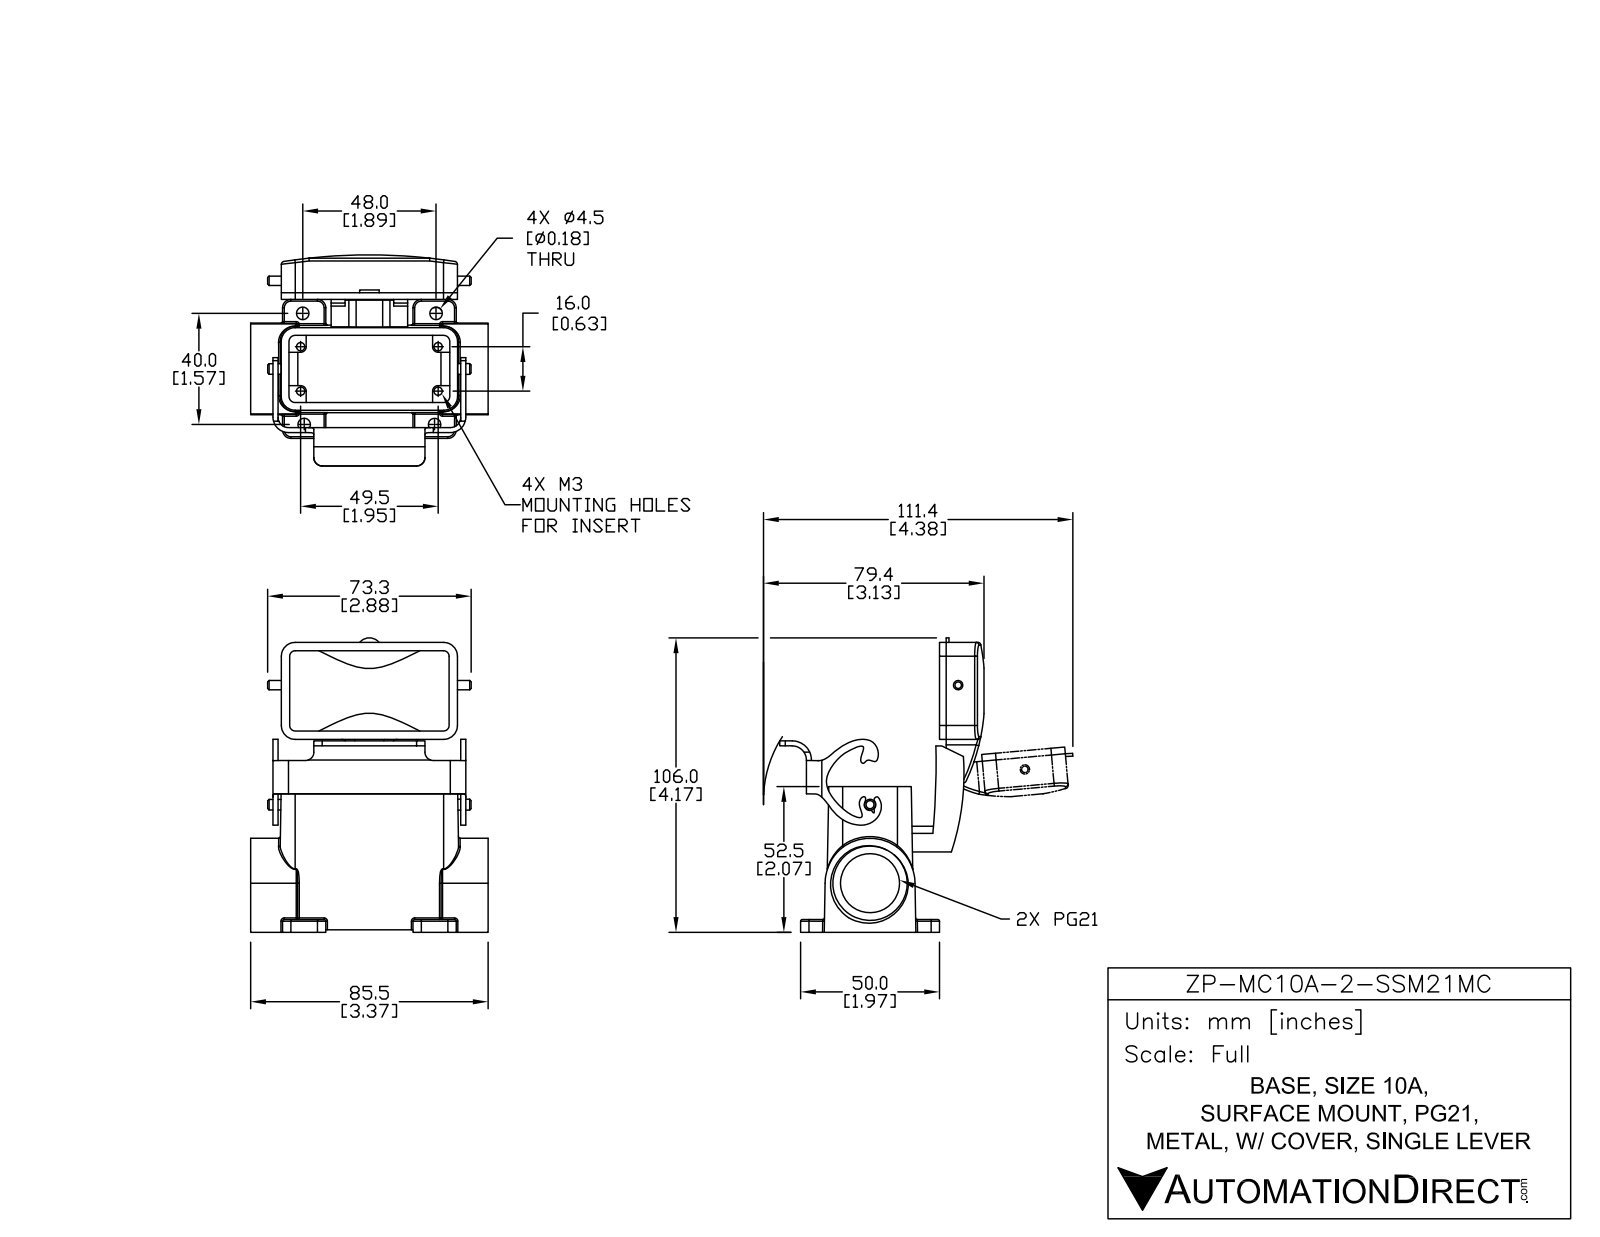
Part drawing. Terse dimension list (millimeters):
name: ZP-MC10A-2-SSM21MC
written by: SolidWorks 2014 (AUTOMOTIVE_DESIGN)
unit: mm
bodies: 3 solids, 416 faces (145 planar, 177 cylindrical, 94 other)
size: 100.89 × 85.5 × 75.98
volume: 68 116 mm³; area: 46 348 mm²
holes: 4× ⌀3, 4× ⌀4.5, 1× ⌀21.25, 1× ⌀26.75
bosses: 1× ⌀7.5, 1× ⌀3.9, 1× ⌀3.8, 1× ⌀3.35
rounds: 28× R0.6, 12× R3, 10× R2, 6× R5, 5× R1, 2× R3.75, 2× R5.55, 1× R2.1
face distances: 2.77, 2.78, 3, 4.44, 3.52, 1.8, 27, 20, 0.74, 0.92
hole spacings: 12.02, 12.07, 16, 28.01, 28.03, 40, 49.5, 49.69
